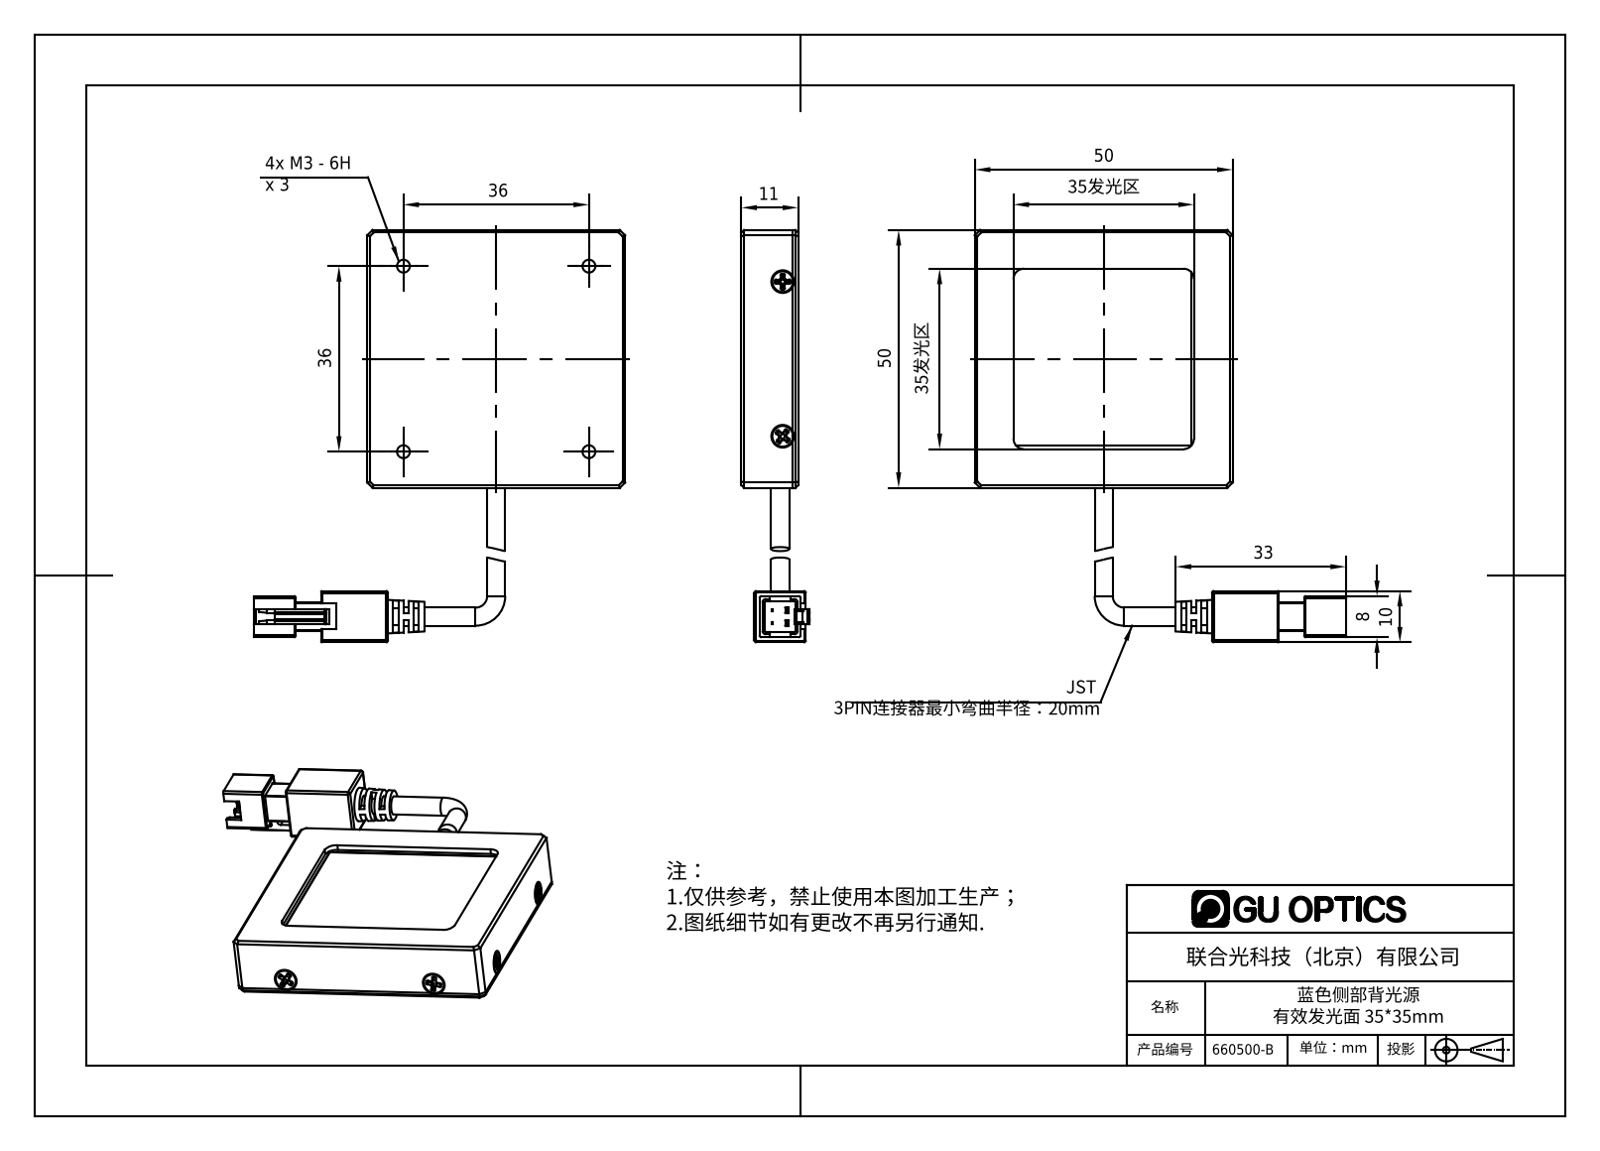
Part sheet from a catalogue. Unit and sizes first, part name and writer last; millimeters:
Units: millimetres
Overall size (bounding box): 80.2 × 72 × 13.2
Round holes (diameter × count): ⌀1.6 ×4, ⌀2.4 ×4, ⌀2.5 ×4, ⌀3.6 ×1
Round bosses / shafts (diameter × count): ⌀2 ×4, ⌀3.5 ×2
Partial cylindrical surfaces — rounded edges, fillets, slot ends (radius × count): R0.2 ×109, R0.1 ×15, R0.4 ×12, R1 ×7, R2 ×4, R0.3 ×1, R0.68 ×1, R1.4 ×1
Main face-to-face distances: 4.2, 1, 5.5, 4.1, 1.2, 4.5, 4.3, 1.1, 5.3, 4
Hole centre spacings: 36, 15.01, 30, 50.91
Volume: 23 999 mm³ · Surface area: 35 401 mm²
Bodies: 37 solids, 955 faces (540 planar, 232 cylindrical, 183 other)
Part name (STEP PRODUCT): 660500-B
STEP written by: SolidWorks 2016 (AUTOMOTIVE_DESIGN)
